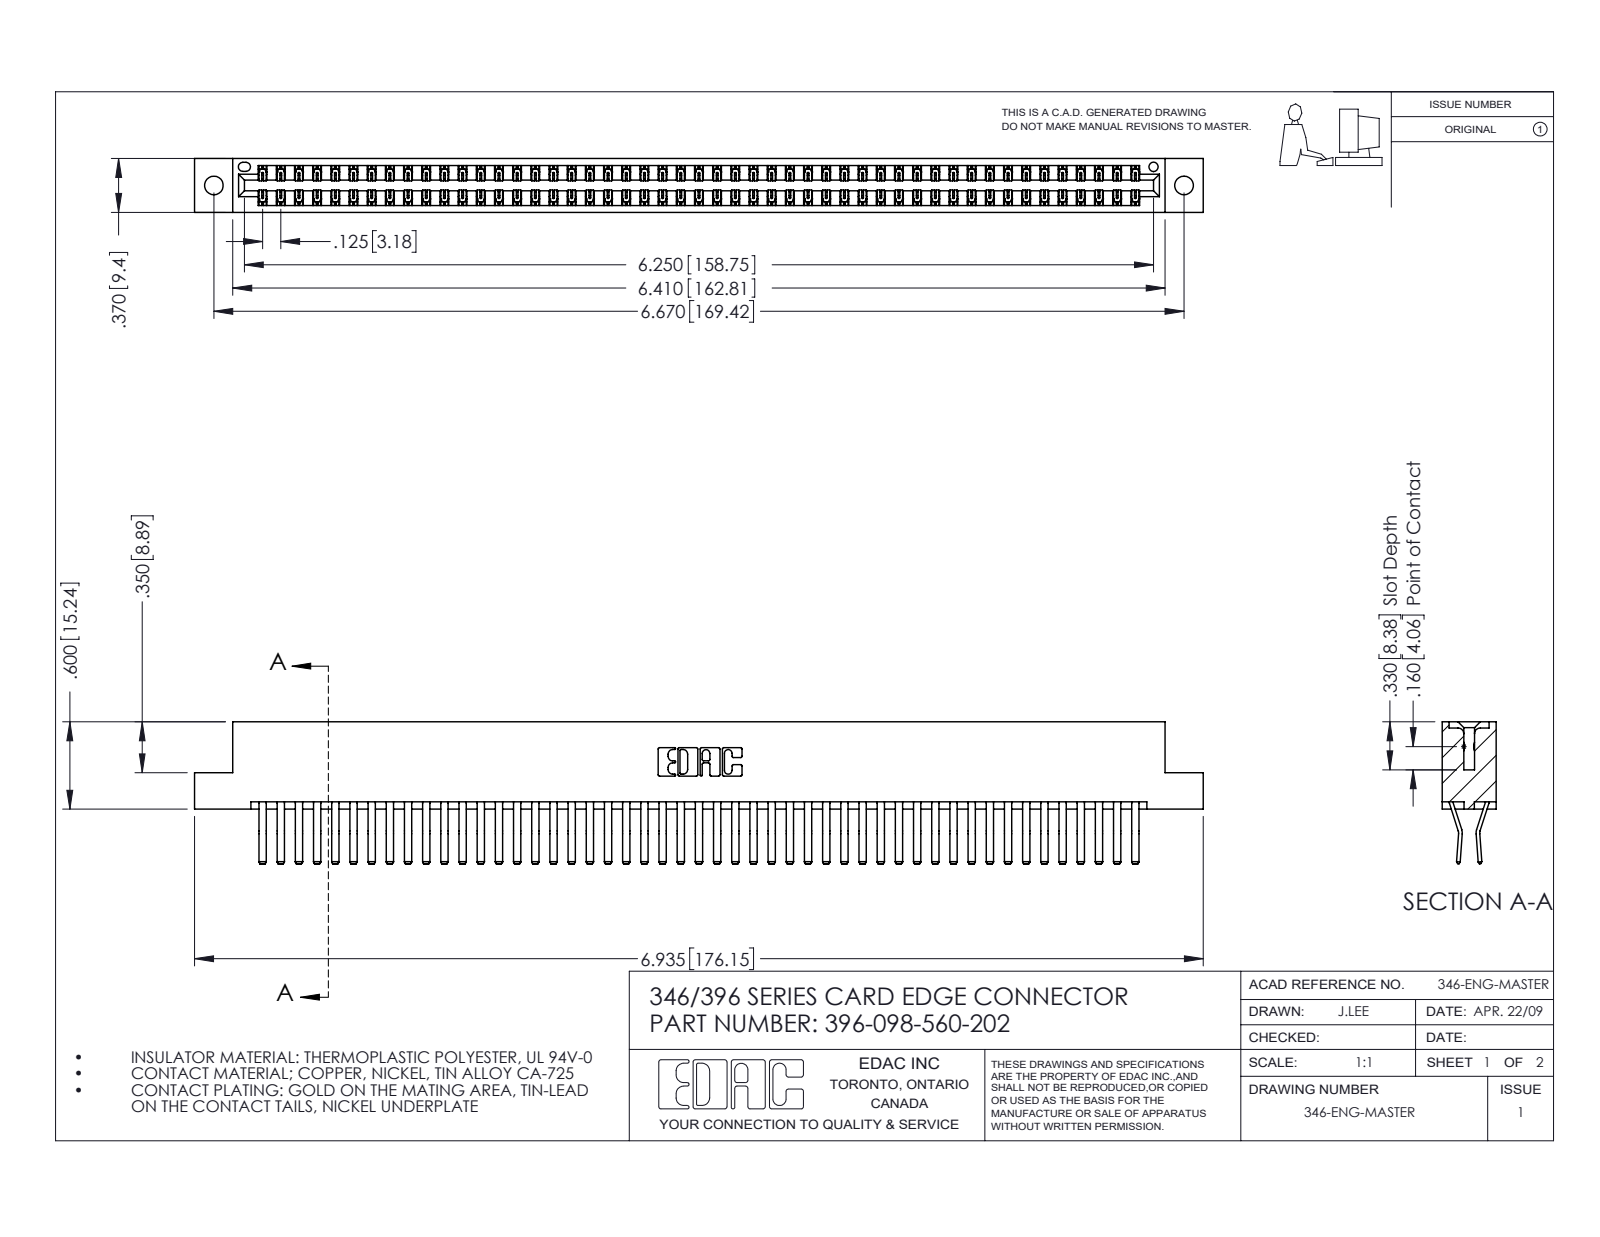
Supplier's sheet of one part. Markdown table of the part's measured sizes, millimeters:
| quantity | value |
| --- | --- |
| part name | 345-292-001_560 Tail; 346 Part_Flush Mounting Lugs - 0.128 Dia; 396-098-560-202 |
| STEP written by | SolidWorks 2016 (CONFIG_CONTROL_DESIGN) |
| units | millimeters |
| bodies | 99 solids, 5414 faces (3506 planar, 1908 cylindrical, 0 other) |
| overall size | 176.1 × 24.8 × 9.4 |
| volume | 17 830 mm³ |
| surface area | 26 070 mm² |
| round holes (diameter × count) | 3.3 × 2, 1.6 × 1 |
| partial cylindrical surfaces (radius × count) | 0.2 × 147, 0.3 × 22, 0.2 × 6, 0.8 × 6, 0.7 × 3, 0.3 × 2, 0.4 × 2, 0.6 × 2 |
| main face-to-face distances | 1.2, 8.2, 9.4, 0.6, 6.4, 1.8, 7.6, 7, 3.8, 5.6 |
| hole center spacings | 6.2, 164.1, 169.4 |
